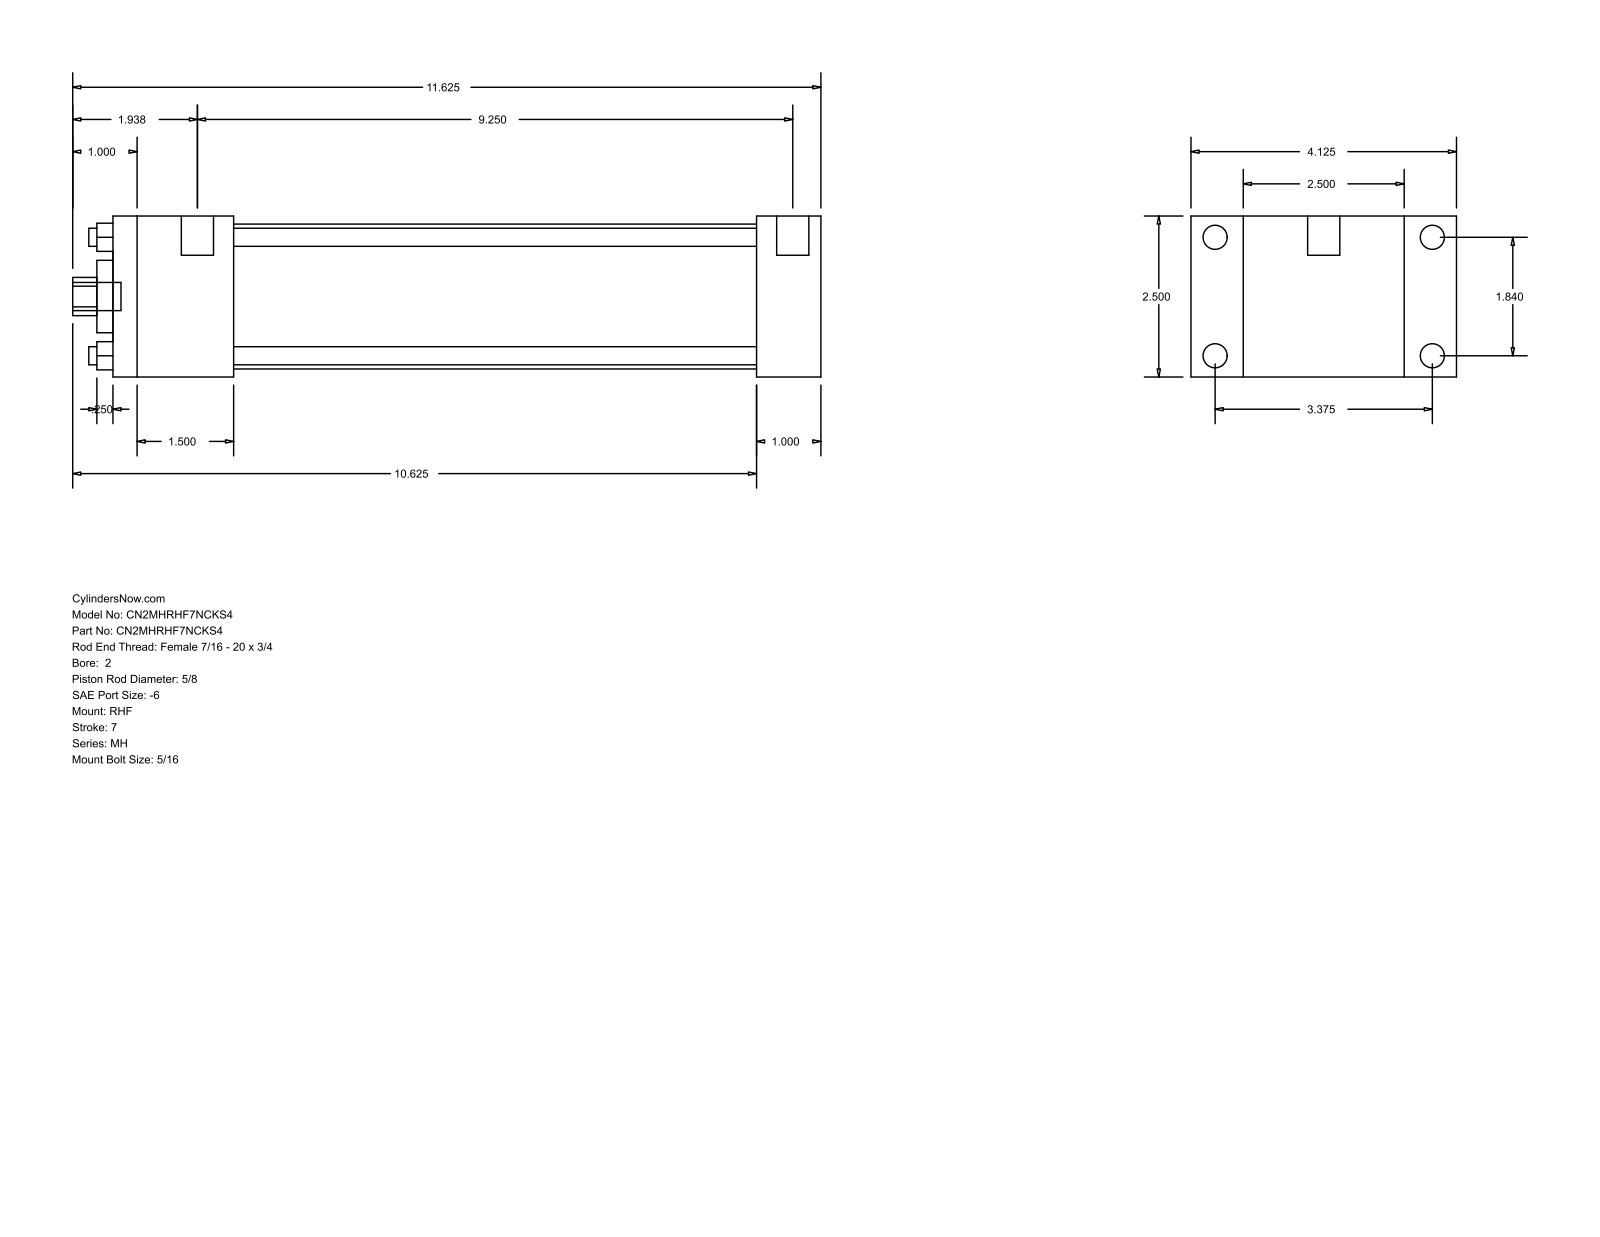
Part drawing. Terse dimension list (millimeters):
name: MH_RHF__0200_0.625
written by: GSSL Pune (CONFIG_CONTROL_DESIGN)
unit: mm
bodies: 0 solids, 88 faces (60 planar, 28 cylindrical, 0 other)
size: 295.27 × 104.78 × 63.5
holes: 4× ⌀7.14, 1× ⌀15.88, 1× ⌀28.57, 1× ⌀57.15
bosses: 4× ⌀9.53, 4× ⌀5.56, 2× ⌀12.7, 1× ⌀11.11
rounds: 1× R7.54
face distances: 63.5, 25.39, 20.64, 84.14, 254, 279.39, 104.78, 47.62, 206.38, 231.77
hole spacings: 33.05, 46.74, 66.1
